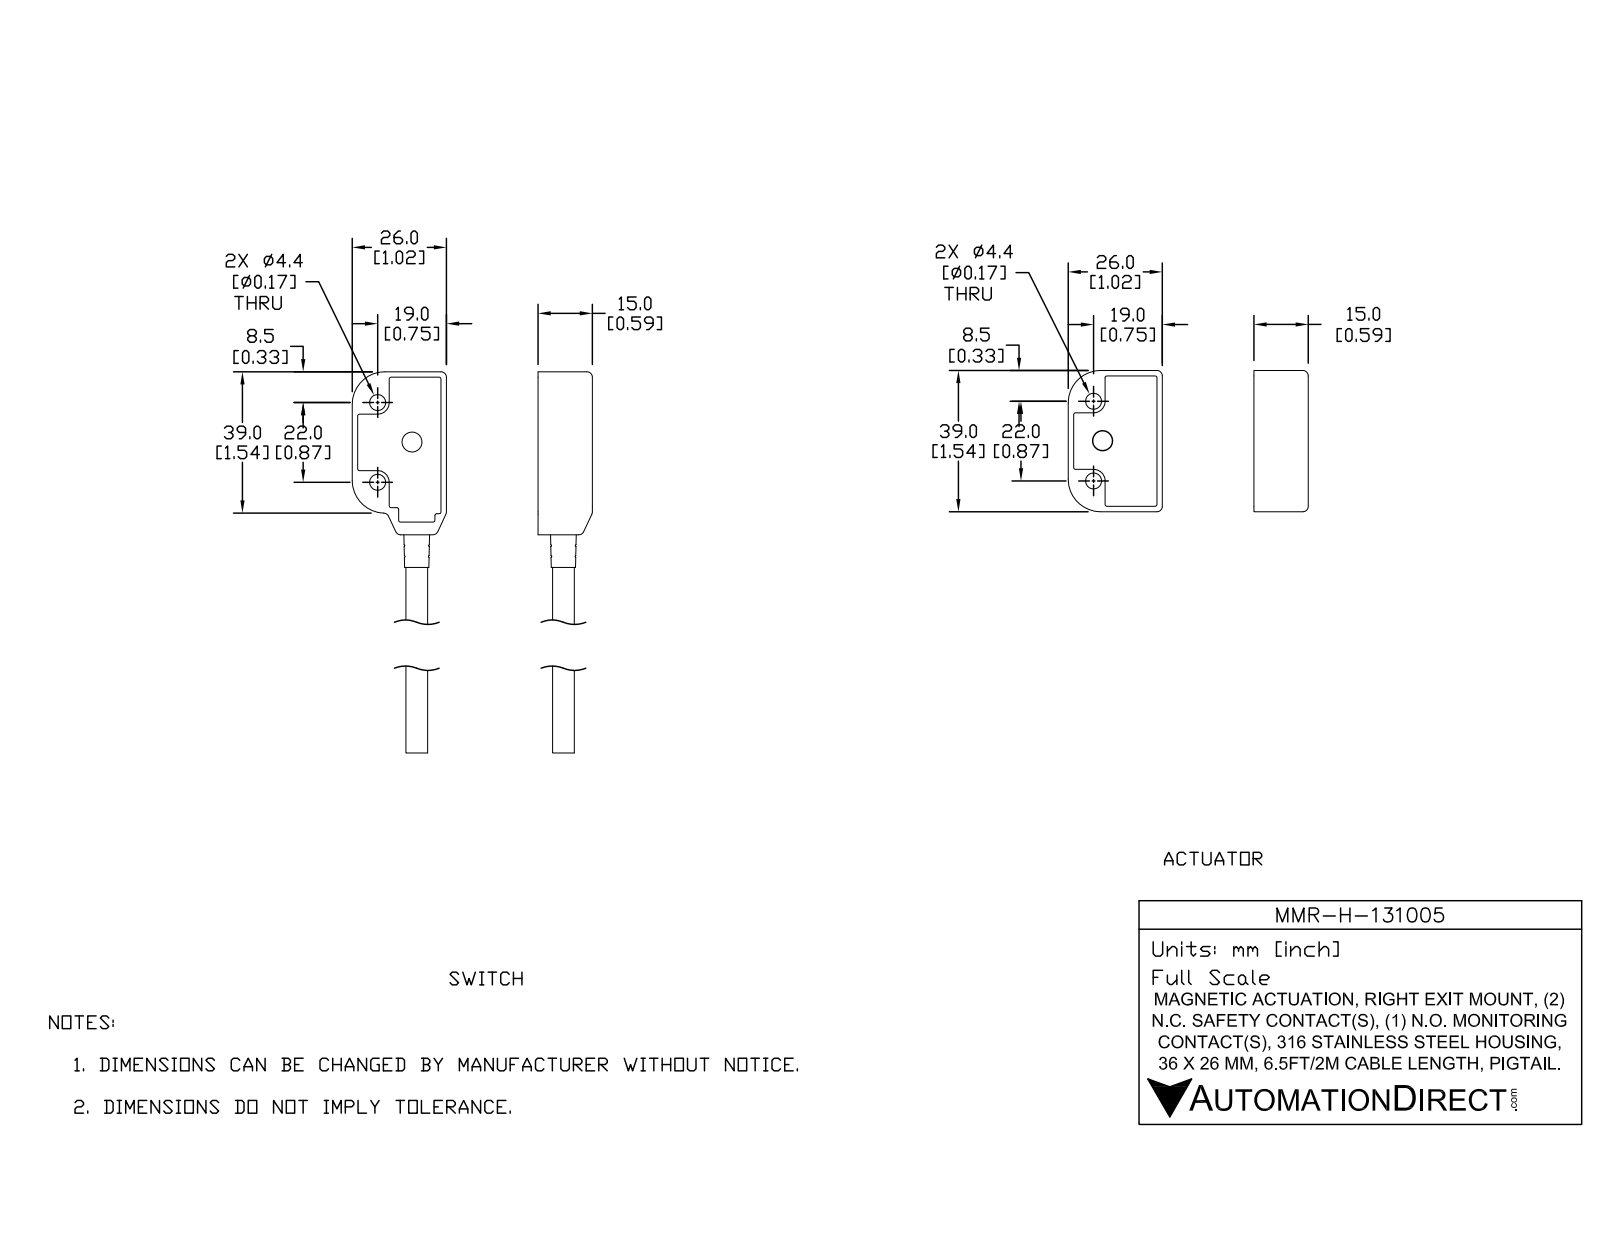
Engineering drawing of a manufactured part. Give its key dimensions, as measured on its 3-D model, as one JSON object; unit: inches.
{"part_name": "MMR-H-131005_2; MMR-H-131005_1; MMR-H-131005", "step_written_by": "SolidWorks 2017 (AUTOMOTIVE_DESIGN)", "units": "inches", "bodies": {"solids": 7, "faces": 584, "planar": 173, "cylindrical": 224, "other": 187}, "overall_size": [7.803, 2.087, 0.591], "volume_in3": 1.232, "surface_area_in2": 30.25, "round_holes": [[0.173, 4], [0.197, 2], [0.232, 1], [0.283, 1]], "round_bosses_or_shafts": [[0.079, 2], [0.339, 1], [0.299, 1], [0.28, 1], [0.236, 1], [0.118, 1]], "partial_cylinders_radius": [[0.02, 82], [0.012, 26], [0.059, 15], [0.008, 8], [0.157, 6], [0.126, 4], [0.13, 4], [0.181, 4]], "face_to_face_distances": [0.059, 0.575, 0.516, 0.461, 0.098, 0.52, 0.055, 0.591, 0.531, 0.965], "hole_center_spacings": [0.866, 1.535, 1.763, 0.44, 0.448, 0.569, 0.575, 1.063]}
